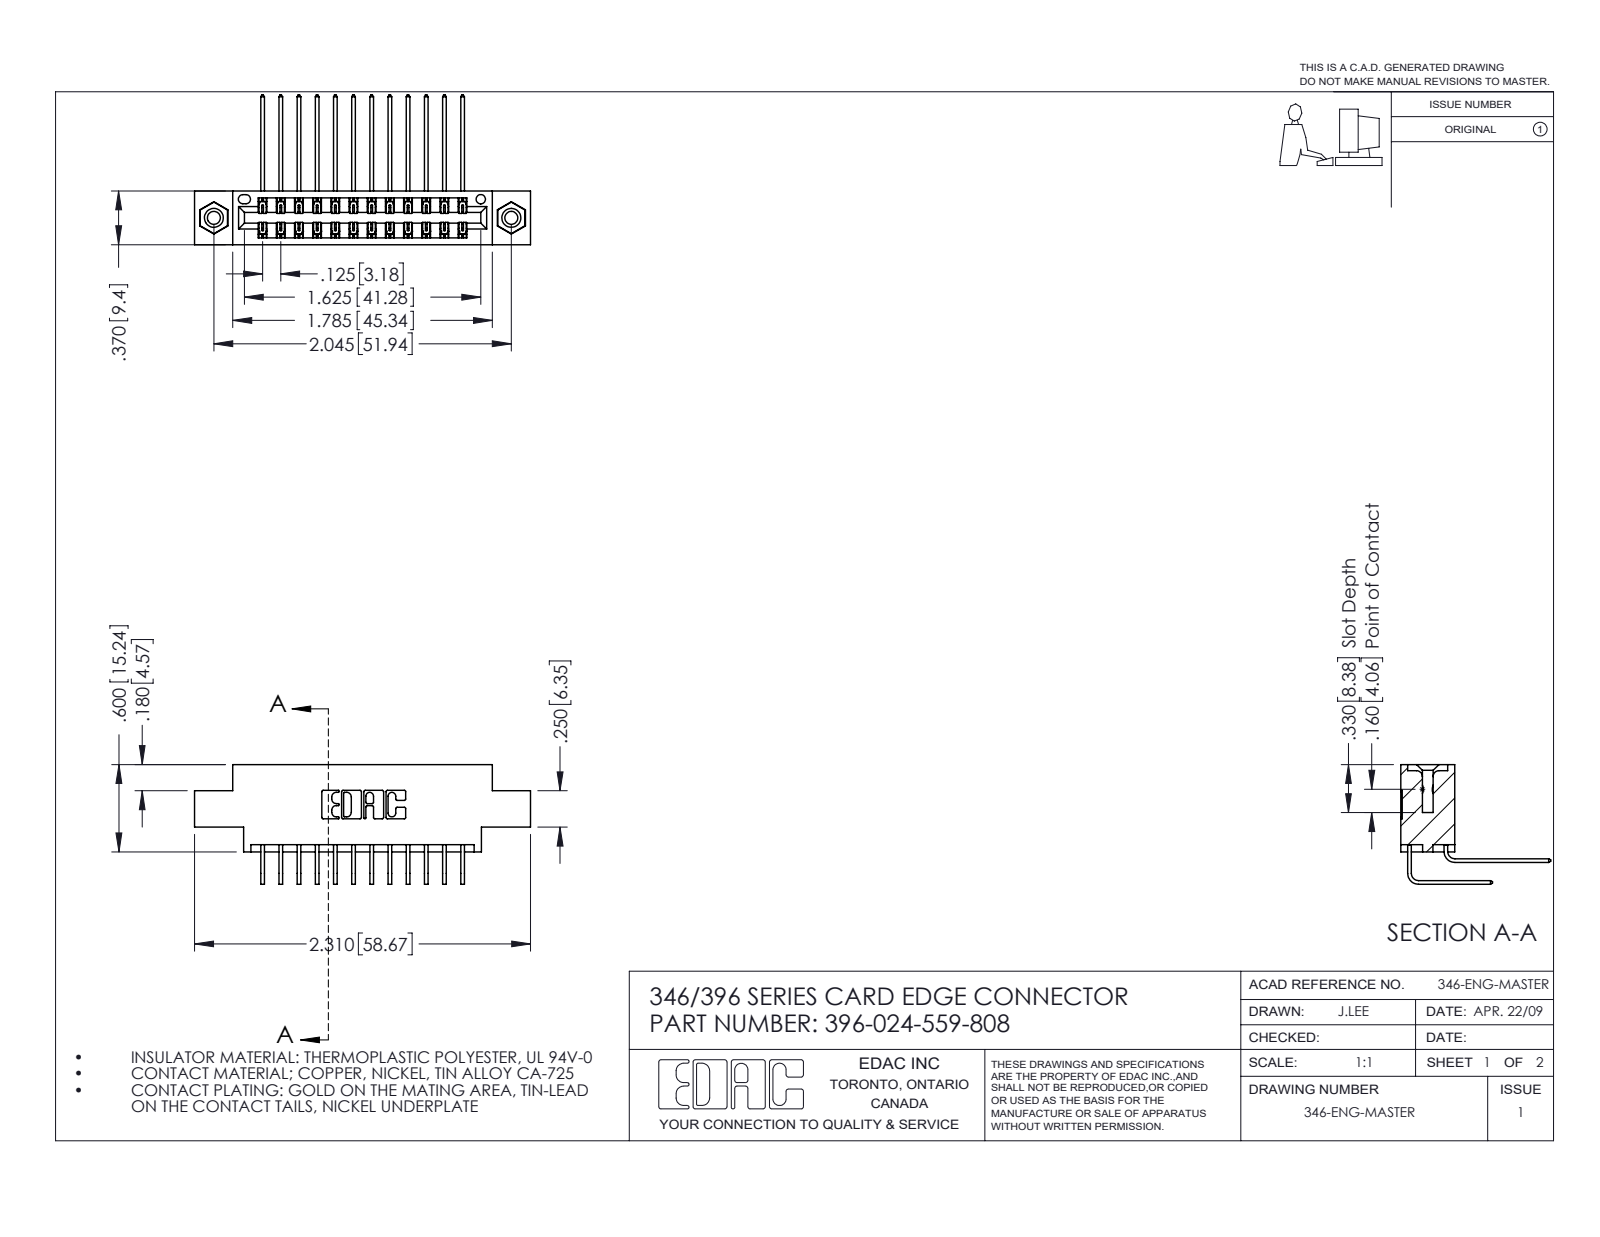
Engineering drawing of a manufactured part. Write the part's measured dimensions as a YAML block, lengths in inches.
part_name: "396-024-559-808; 345-292-001_558 559 Tail - 1; 346 Part_0.170 Offset - 0.156 Dia-TI; 345-250-001_345-250-003-102 (+1 more)"
step_written_by: "SolidWorks 2016 (CONFIG_CONTROL_DESIGN)"
units: inches
bodies: {solids: 27, faces: 1482, planar: 1000, cylindrical: 466, other: 16}
overall_size: [2.31, 1.03, 0.823]
volume: 0.334
surface_area: 12.25
round_holes:
  - {diameter: 0.089, count: 2}
  - {diameter: 0.125, count: 2}
  - {diameter: 0.156, count: 2}
  - {diameter: 0.064, count: 1}
round_bosses_or_shafts:
  - {diameter: 0.155, count: 2}
partial_cylinders:
  - {radius: 0.006, count: 36}
  - {radius: 0.01, count: 22}
  - {radius: 0.007, count: 6}
  - {radius: 0.031, count: 6}
  - {radius: 0.026, count: 3}
  - {radius: 0.014, count: 2}
  - {radius: 0.022, count: 2}
  - {radius: 0.024, count: 2}
face_to_face_distances: [0.048, 0.25, 0.322, 0.37, 0.025, 0.072, 0.298, 0.222, 0.148, 0.275]
hole_center_spacings: [0.246, 1.839, 2.045]
